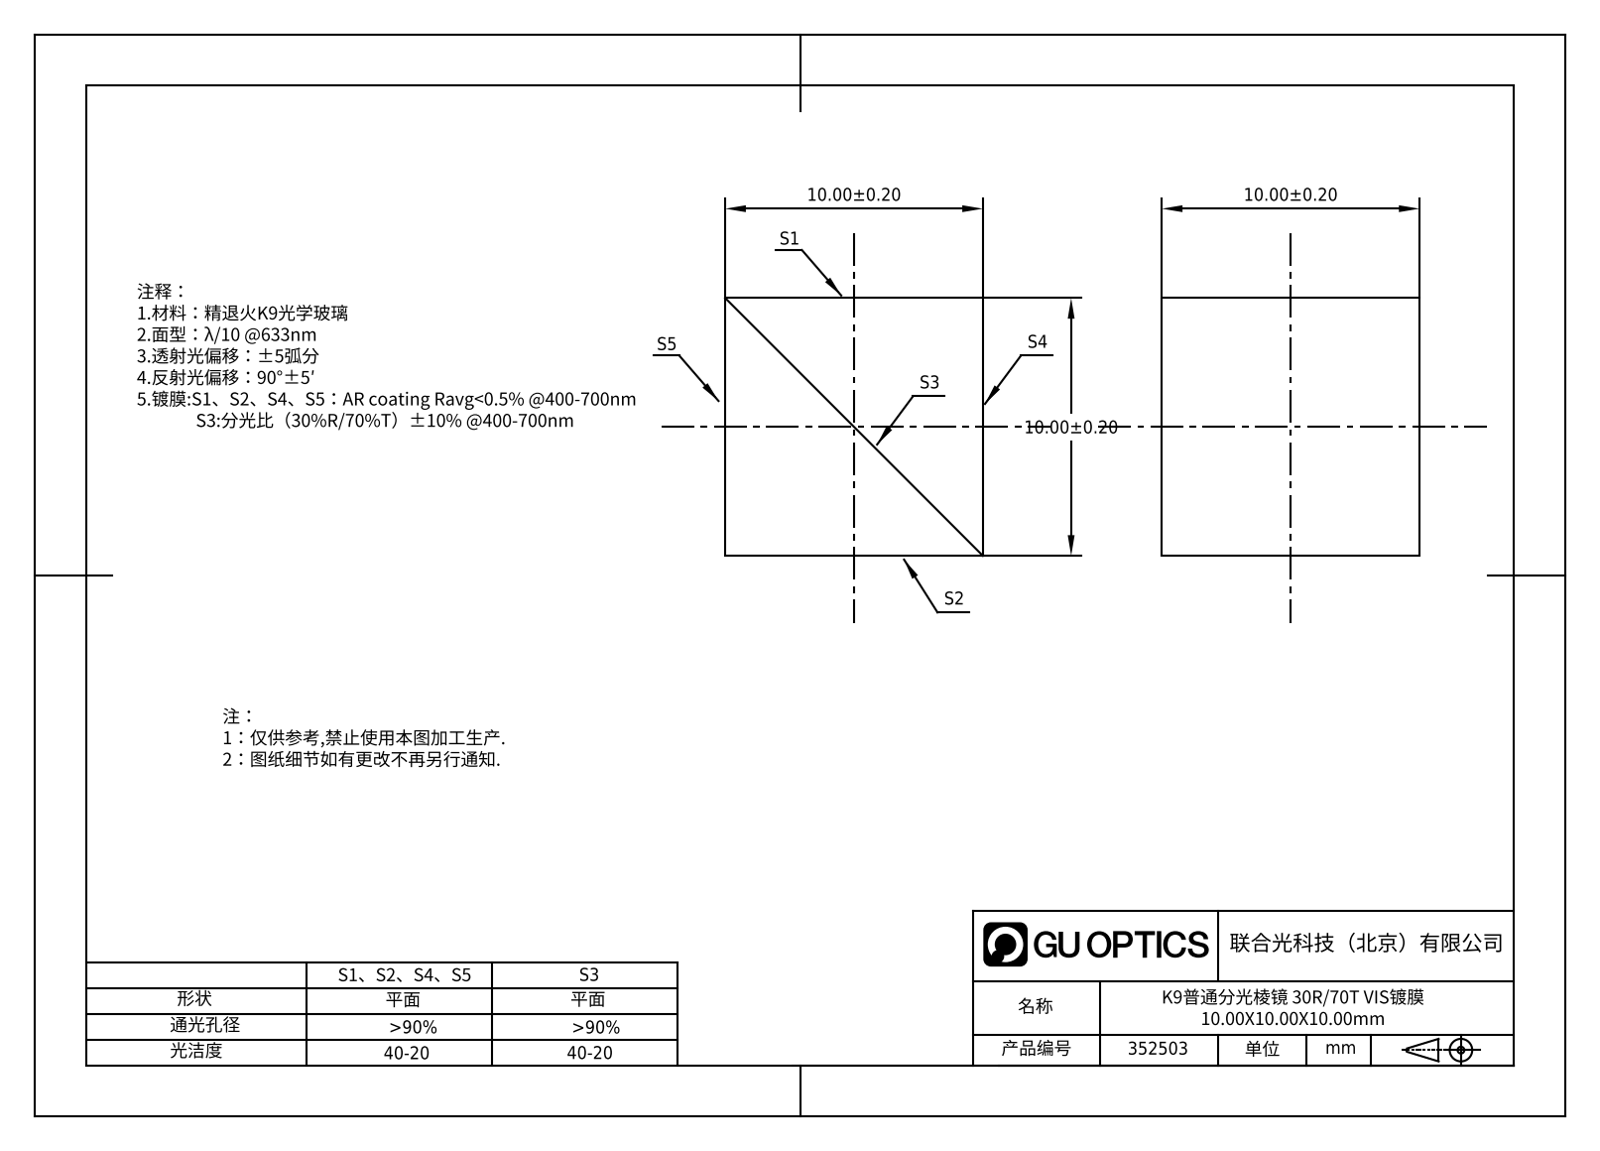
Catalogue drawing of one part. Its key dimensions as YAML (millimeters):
part_name: "352503"
step_written_by: "SolidWorks 2016 (AUTOMOTIVE_DESIGN)"
units: millimeters
bodies: {solids: 2, faces: 10, planar: 10, cylindrical: 0, other: 0}
overall_size: [10, 10, 10]
volume: 1000
surface_area: 883
face_to_face_distances: [10]
